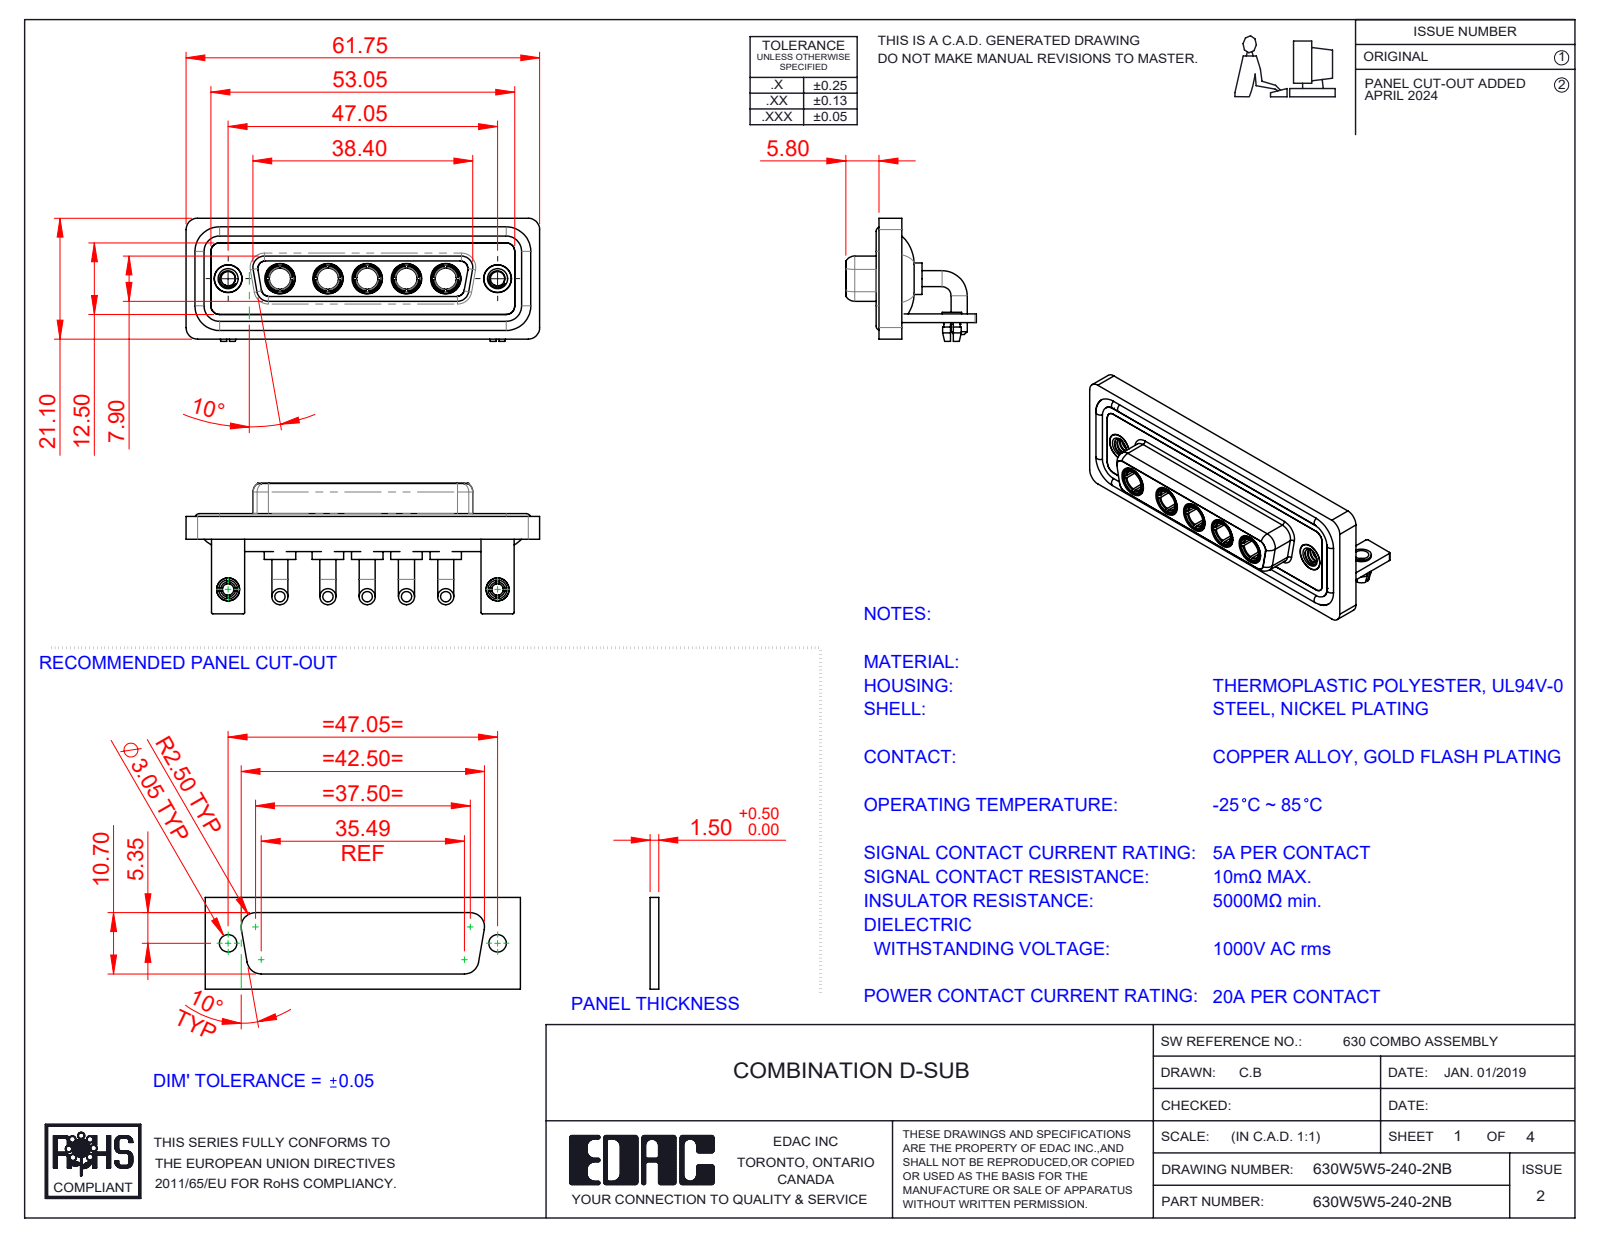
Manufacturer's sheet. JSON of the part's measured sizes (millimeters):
{"part_name": "630Combo Waterproof Housing_25 Contacts; Power Socket_20A RA; 630Combo Shell Rear_25 Contacts; 630Combo Threaded Rivet_A (+5 more)", "step_written_by": "SolidWorks 2023 (CONFIG_CONTROL_DESIGN)", "units": "millimeters", "bodies": {"solids": 21, "faces": 910, "planar": 318, "cylindrical": 367, "other": 225}, "overall_size": [61.75, 22.8, 21.5], "volume_mm3": 8830, "surface_area_mm2": 14762, "round_holes": [[4.85, 7], [3.7, 5], [5.3, 5], [2.5, 4], [2, 2], [3.2, 2], [4, 2], [4.05, 2], [5, 2]], "round_bosses_or_shafts": [[2.8, 10], [5.5, 5], [5.2, 5], [4.96, 5], [4.75, 5], [3.75, 5], [1.6, 4], [4.95, 2]], "partial_cylinders_radius": [[2, 19], [1.5, 18], [0.25, 16], [1.35, 8], [1.6, 8], [0.5, 5], [2.1, 5], [0.6, 4]], "face_to_face_distances": [0.4, 1.8, 2.9, 1.5, 3.7, 4.1, 1.1, 1.4, 1.6, 2.5], "hole_center_spacings": [6.86, 9.04, 38.01, 47.05, 6.87, 8.38, 13.72, 13.73]}
